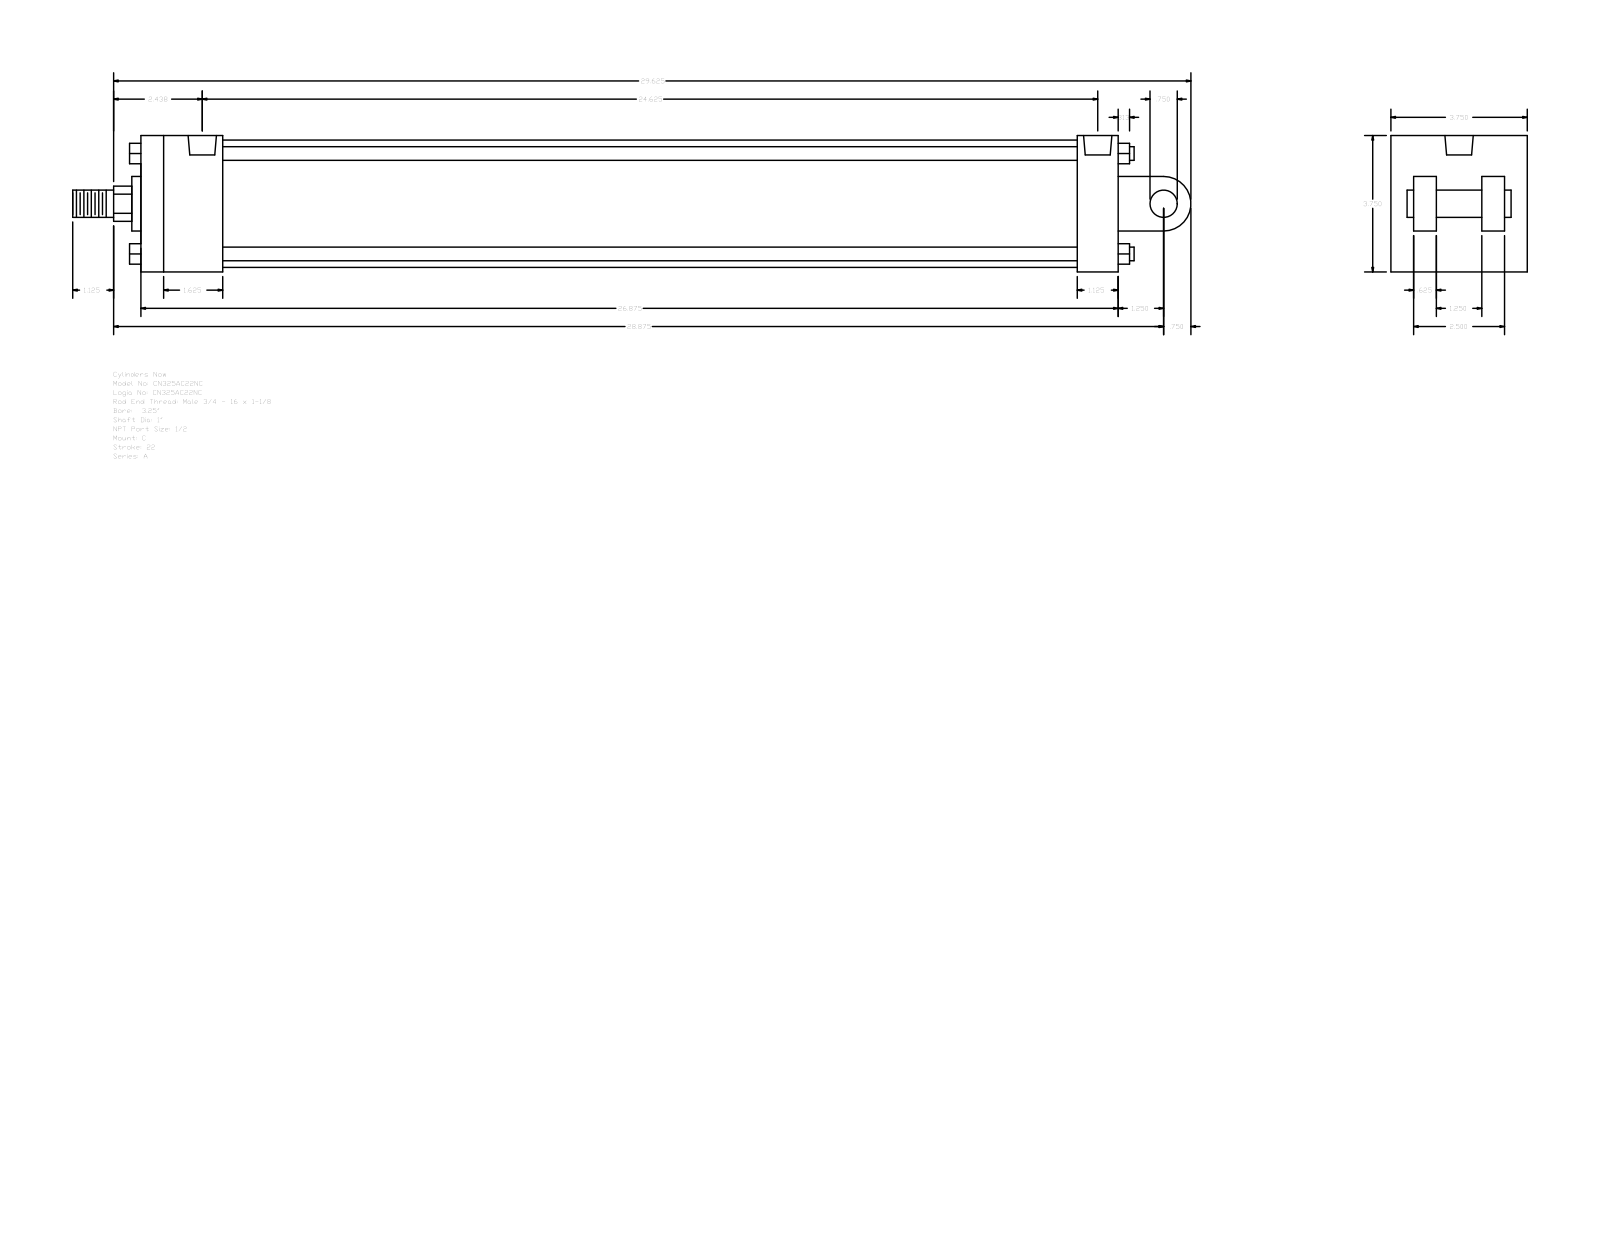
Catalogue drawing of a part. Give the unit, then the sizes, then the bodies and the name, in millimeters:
Units: millimetres
Overall size (bounding box): 781.05 × 95.25 × 95.25
Round holes (diameter × count): ⌀8.73 ×4, ⌀19.77 ×2
Round bosses / shafts (diameter × count): ⌀9.53 ×4, ⌀19.05 ×2, ⌀88.9 ×1, ⌀38.1 ×1, ⌀25.4 ×1
Partial cylindrical surfaces — rounded edges, fillets, slot ends (radius × count): R12.29 ×1, R19.05 ×1
Main face-to-face distances: 95.24, 682.62, 15.87, 63.5, 28.57, 31.74, 79.37, 47.63, 66.67, 654.05
Hole centre spacings: 3.18, 619.12, 622.3, 625.48
Bodies: 0 solids, 135 faces (102 planar, 33 cylindrical, 0 other)
Part name (STEP PRODUCT): A_C__0325_1
STEP written by: GSSL Pune (CONFIG_CONTROL_DESIGN)
